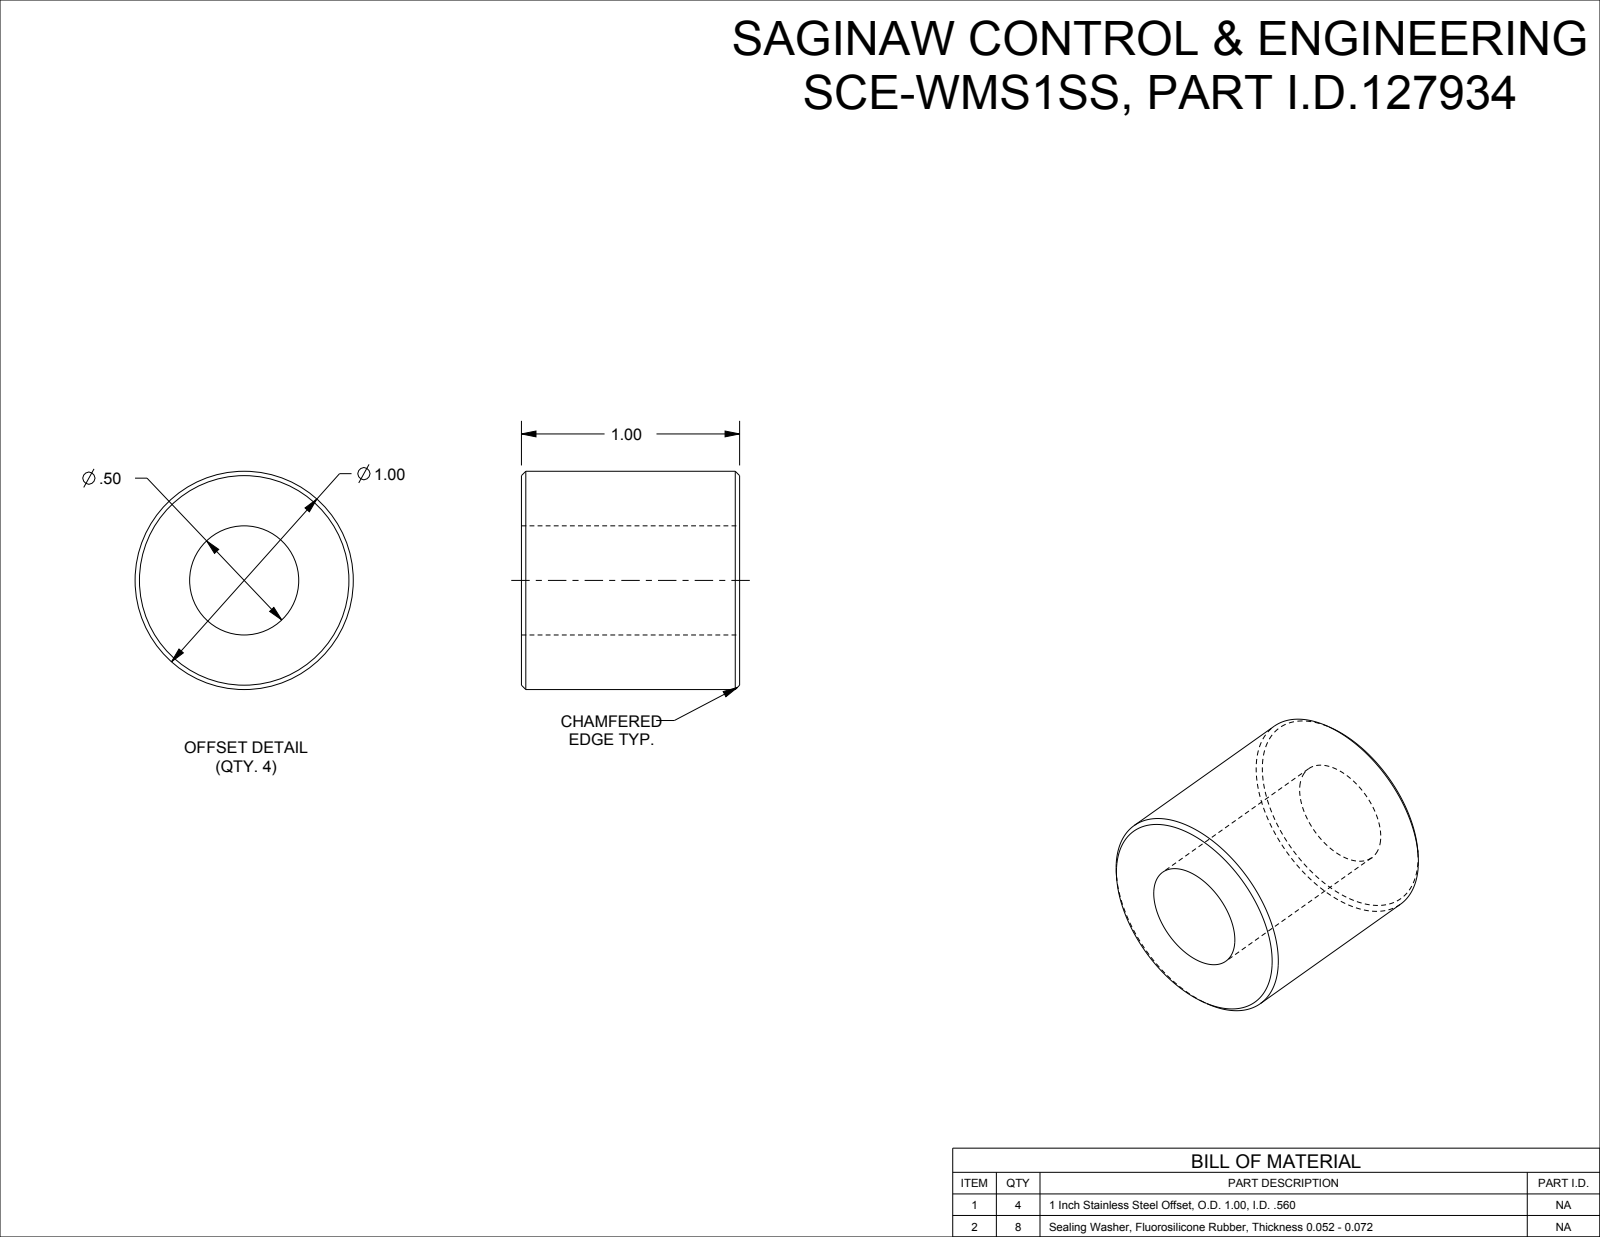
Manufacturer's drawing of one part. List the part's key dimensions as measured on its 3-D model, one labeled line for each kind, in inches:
Part name (STEP PRODUCT): SCE-WMS1SS
STEP written by: SolidWorks 2019 (CONFIG_CONTROL_DESIGN)
Units: inches
Bodies: 3 solids, 14 faces (6 planar, 6 cylindrical, 2 other)
Overall size (bounding box): 1.124 × 1 × 1
Volume: 0.64 in³ · Surface area: 7.946 in²
Round holes (diameter × count): ⌀0.355 ×1, ⌀0.5 ×1
Round bosses / shafts (diameter × count): ⌀1 ×1, ⌀0.812 ×1
Main face-to-face distances: 1, 0.062, 1.062, 1.124
